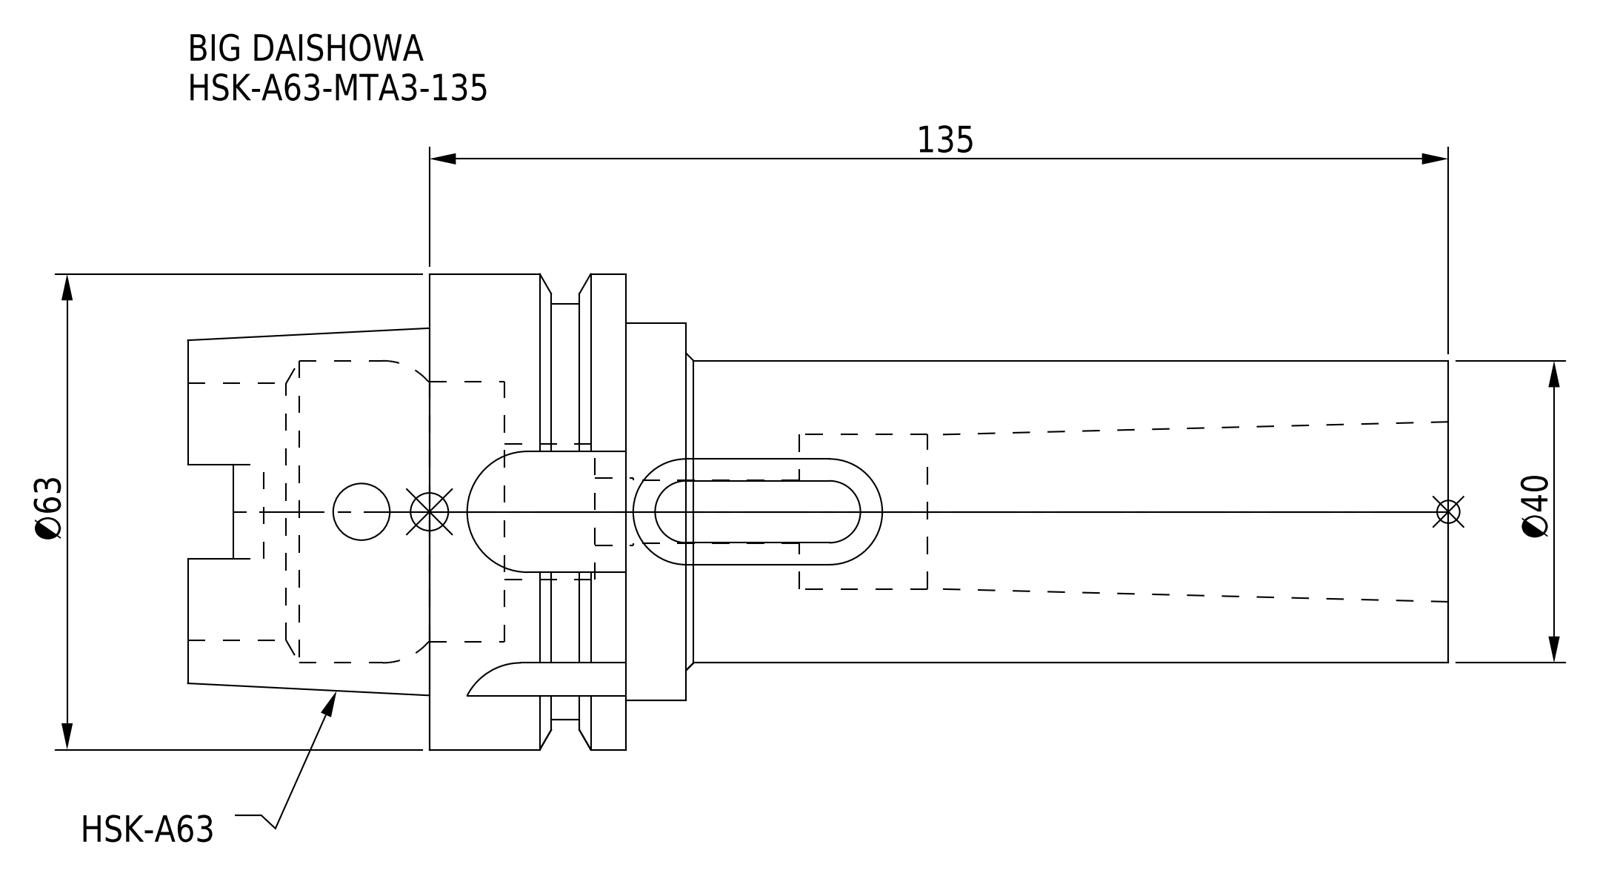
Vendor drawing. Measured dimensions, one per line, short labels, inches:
name: HSK-A63-MTA3-135
written by: CREO PARAMETRIC BY PTC INC, 2016380 (AUTOMOTIVE_DESIGN)
unit: in
bodies: 1 solid, 115 faces (52 planar, 47 cylindrical, 16 other)
size: 6.575 × 2.48 × 2.48
volume: 11.2 in³; area: 67.57 in²
holes: 1× ⌀0.295, 1× ⌀0.331, 1× ⌀0.354, 1× ⌀0.709, 1× ⌀0.807, 1× ⌀1.339, 1× ⌀1.358, 1× ⌀1.575
bosses: 1× ⌀2.48, 1× ⌀2.165, 1× ⌀1.969
rounds: 4× R0.113, 4× R0.315, 2× R0.161, 2× R0.276
face distances: 1.024, 0.323, 4.291, 5.315, 4.923, 0.632, 0.392, 1.26, 6.575, 2.283
